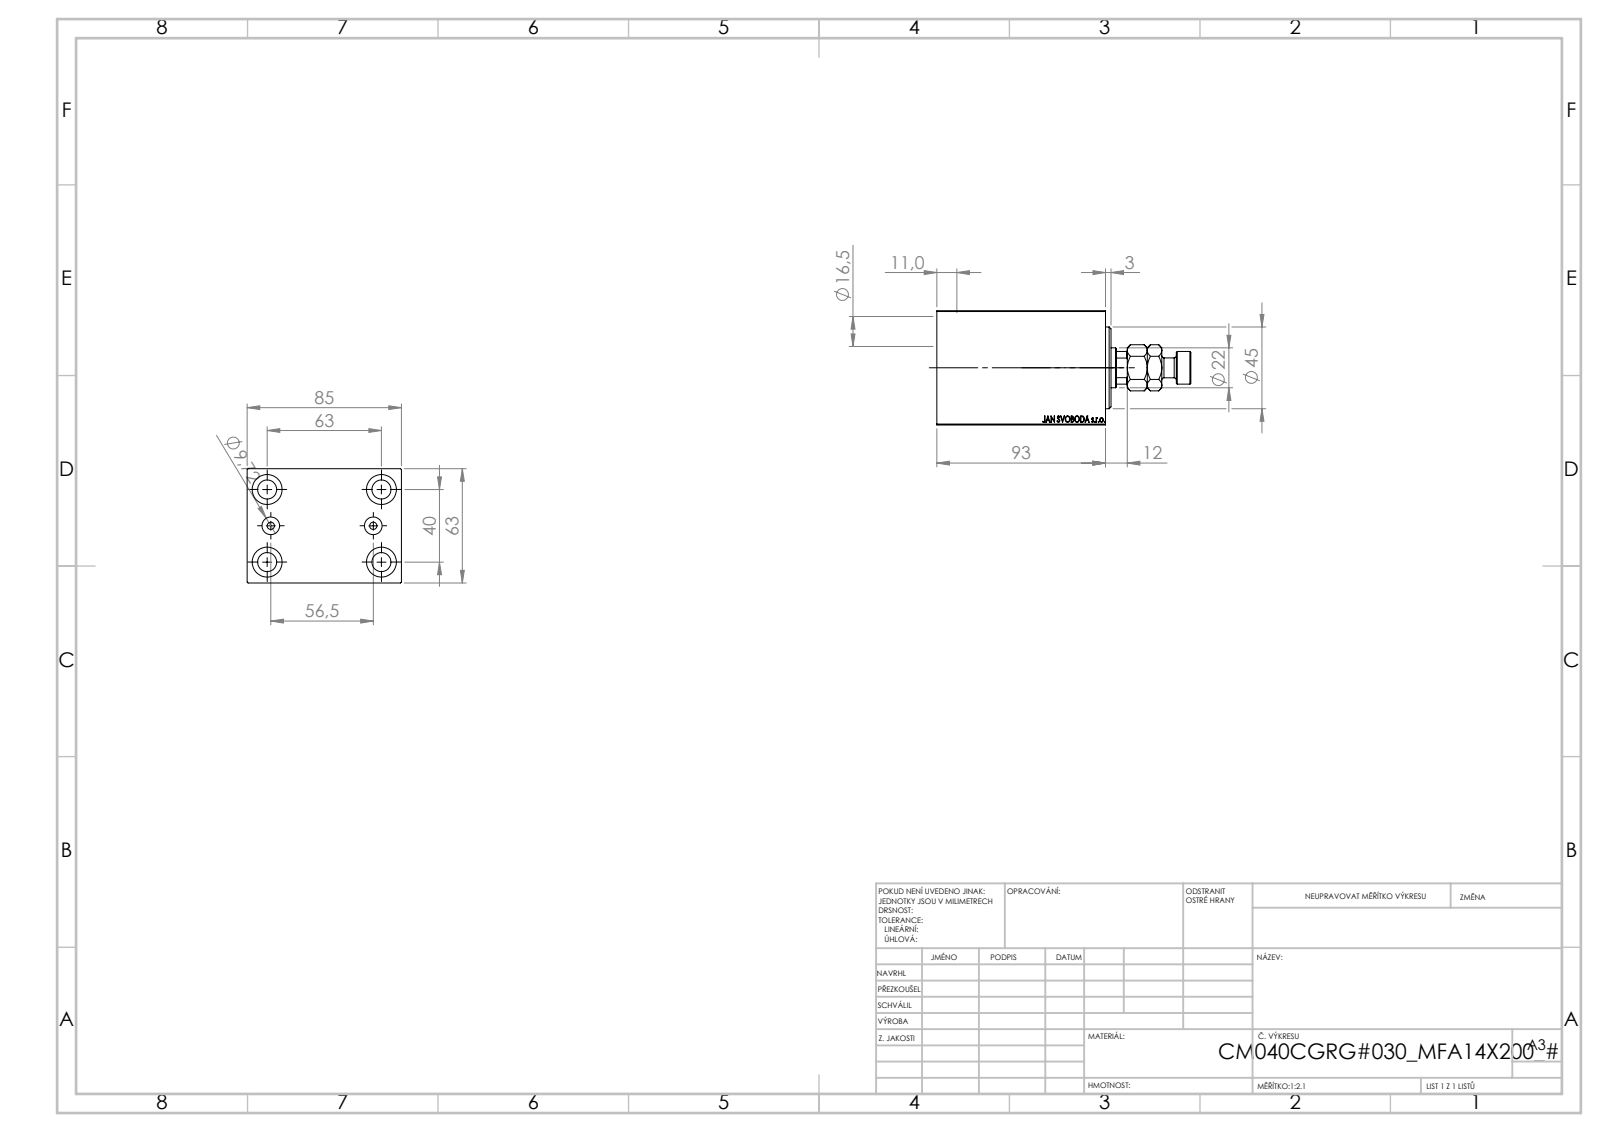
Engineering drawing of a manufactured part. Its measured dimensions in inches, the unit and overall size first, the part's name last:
Units: inches
Overall size (bounding box): 5.512 × 3.346 × 2.48
Round holes (diameter × count): ⌀0.413 ×4, ⌀0.65 ×4, ⌀0.157 ×2, ⌀0.383 ×2, ⌀0.492 ×1, ⌀0.866 ×1, ⌀1.004 ×1, ⌀1.575 ×1, ⌀1.654 ×1, ⌀1.772 ×1
Round bosses / shafts (diameter × count): ⌀0.709 ×1, ⌀0.433 ×1
Partial cylindrical surfaces — rounded edges, fillets, slot ends (radius × count): R0.413 ×1
Main face-to-face distances: 2.48, 3.346, 0.472, 3.189, 3.661, 0.039, 2.717, 1.654, 0.433, 3.228
Hole centre spacings: 1.469, 0.791, 0.807, 1.575, 2.434, 2.48, 2.528, 2.938
Volume: 26.87 in³ · Surface area: 131.5 in²
Bodies: 4 solids, 910 faces (424 planar, 60 cylindrical, 426 other)
Part name (STEP PRODUCT): V450CM_VC_B; V450CM_C_VCP; MFA; V450CM_C_Body
STEP written by: SolidWorks 2019 (CONFIG_CONTROL_DESIGN)
